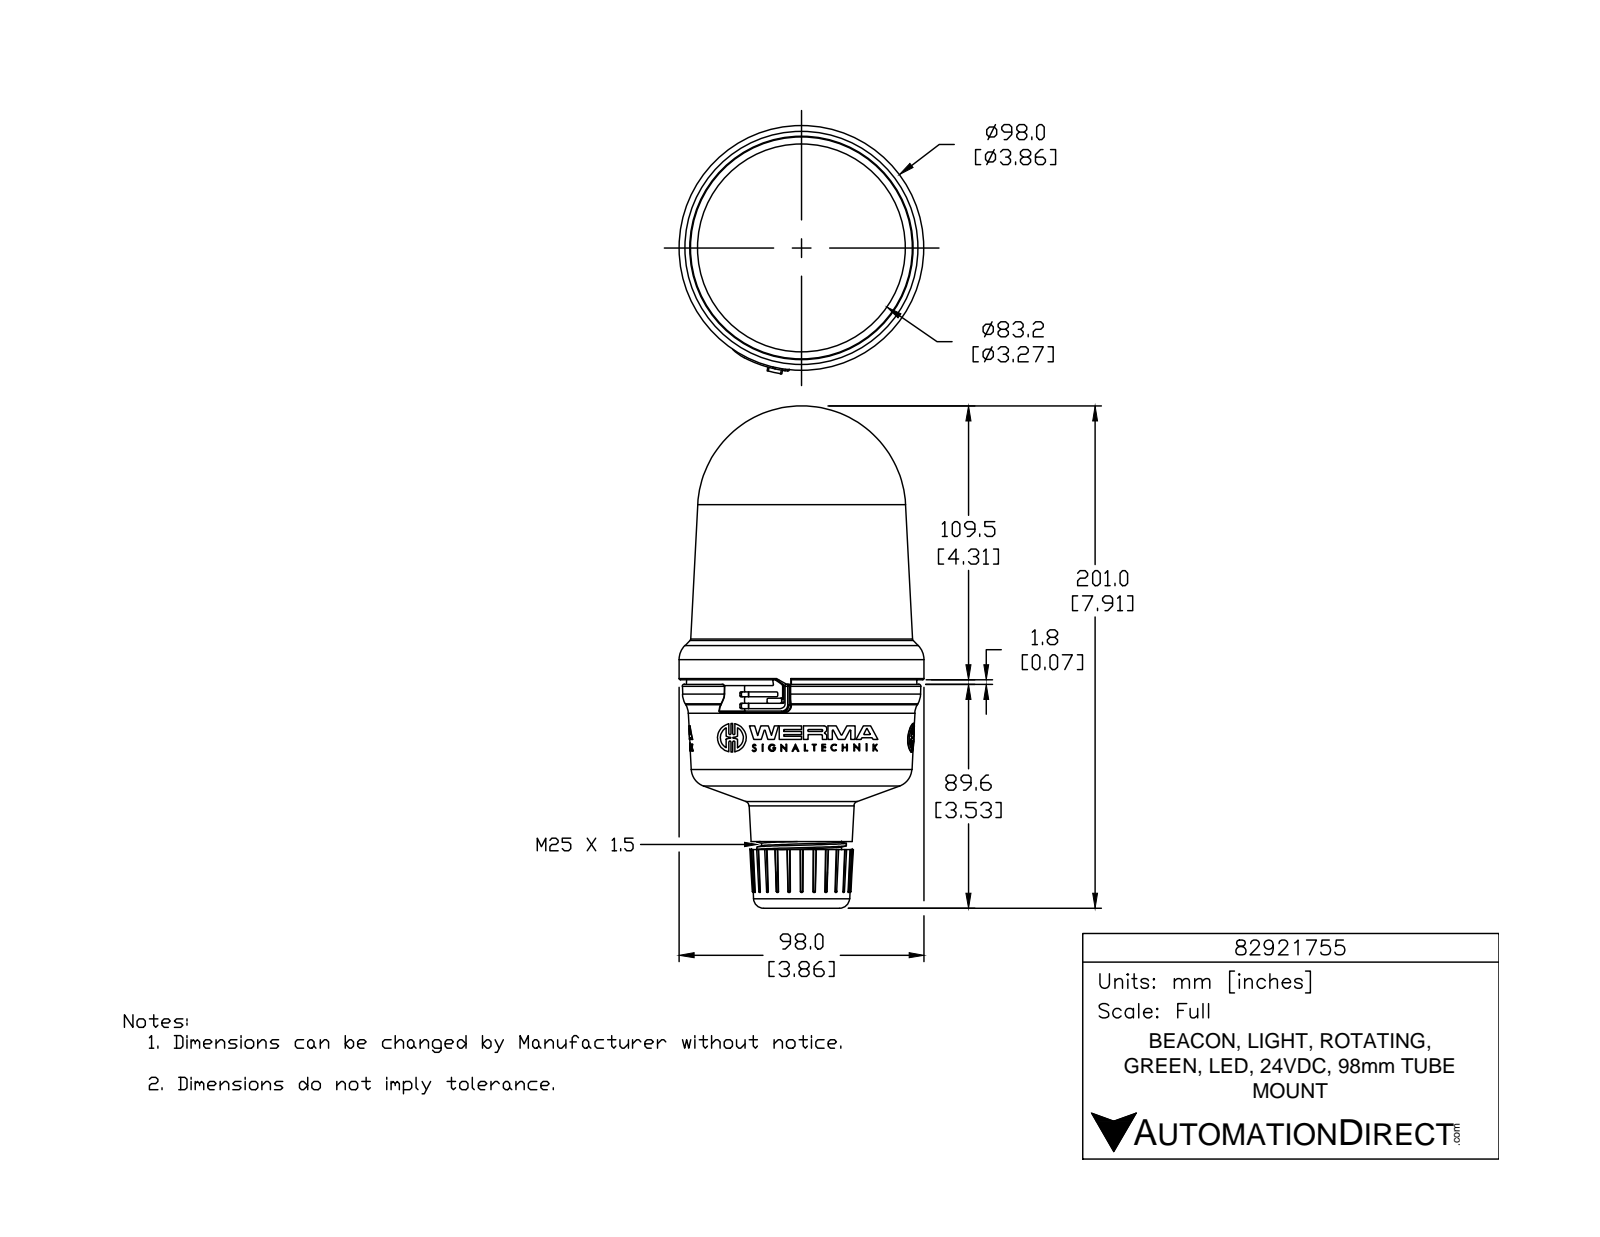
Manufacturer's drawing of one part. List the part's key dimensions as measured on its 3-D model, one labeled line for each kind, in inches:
Part name (STEP PRODUCT): 82921755
STEP written by: SolidWorks 2015 (AUTOMOTIVE_DESIGN)
Units: inches
Bodies: 1 solid, 1006 faces (554 planar, 189 cylindrical, 263 other)
Overall size (bounding box): 7.914 × 3.912 × 3.858
Volume: 54.7 in³ · Surface area: 91.39 in²
Round holes (diameter × count): ⌀0.078 ×3, ⌀1.013 ×1, ⌀1.024 ×1
Round bosses / shafts (diameter × count): ⌀0.452 ×3, ⌀0.113 ×3, ⌀3.858 ×1, ⌀1.409 ×1, ⌀1.261 ×1
Partial cylindrical surfaces — rounded edges, fillets, slot ends (radius × count): R0.02 ×12, R0.007 ×9, R0.007 ×6, R0.016 ×6, R0.016 ×6, R0.016 ×6, R0.262 ×6, R0.006 ×3
Main face-to-face distances: 2.214, 0.462, 2.676, 0.335, 0.127, 2.548, 2.603, 2.476, 2.141, 0.073
